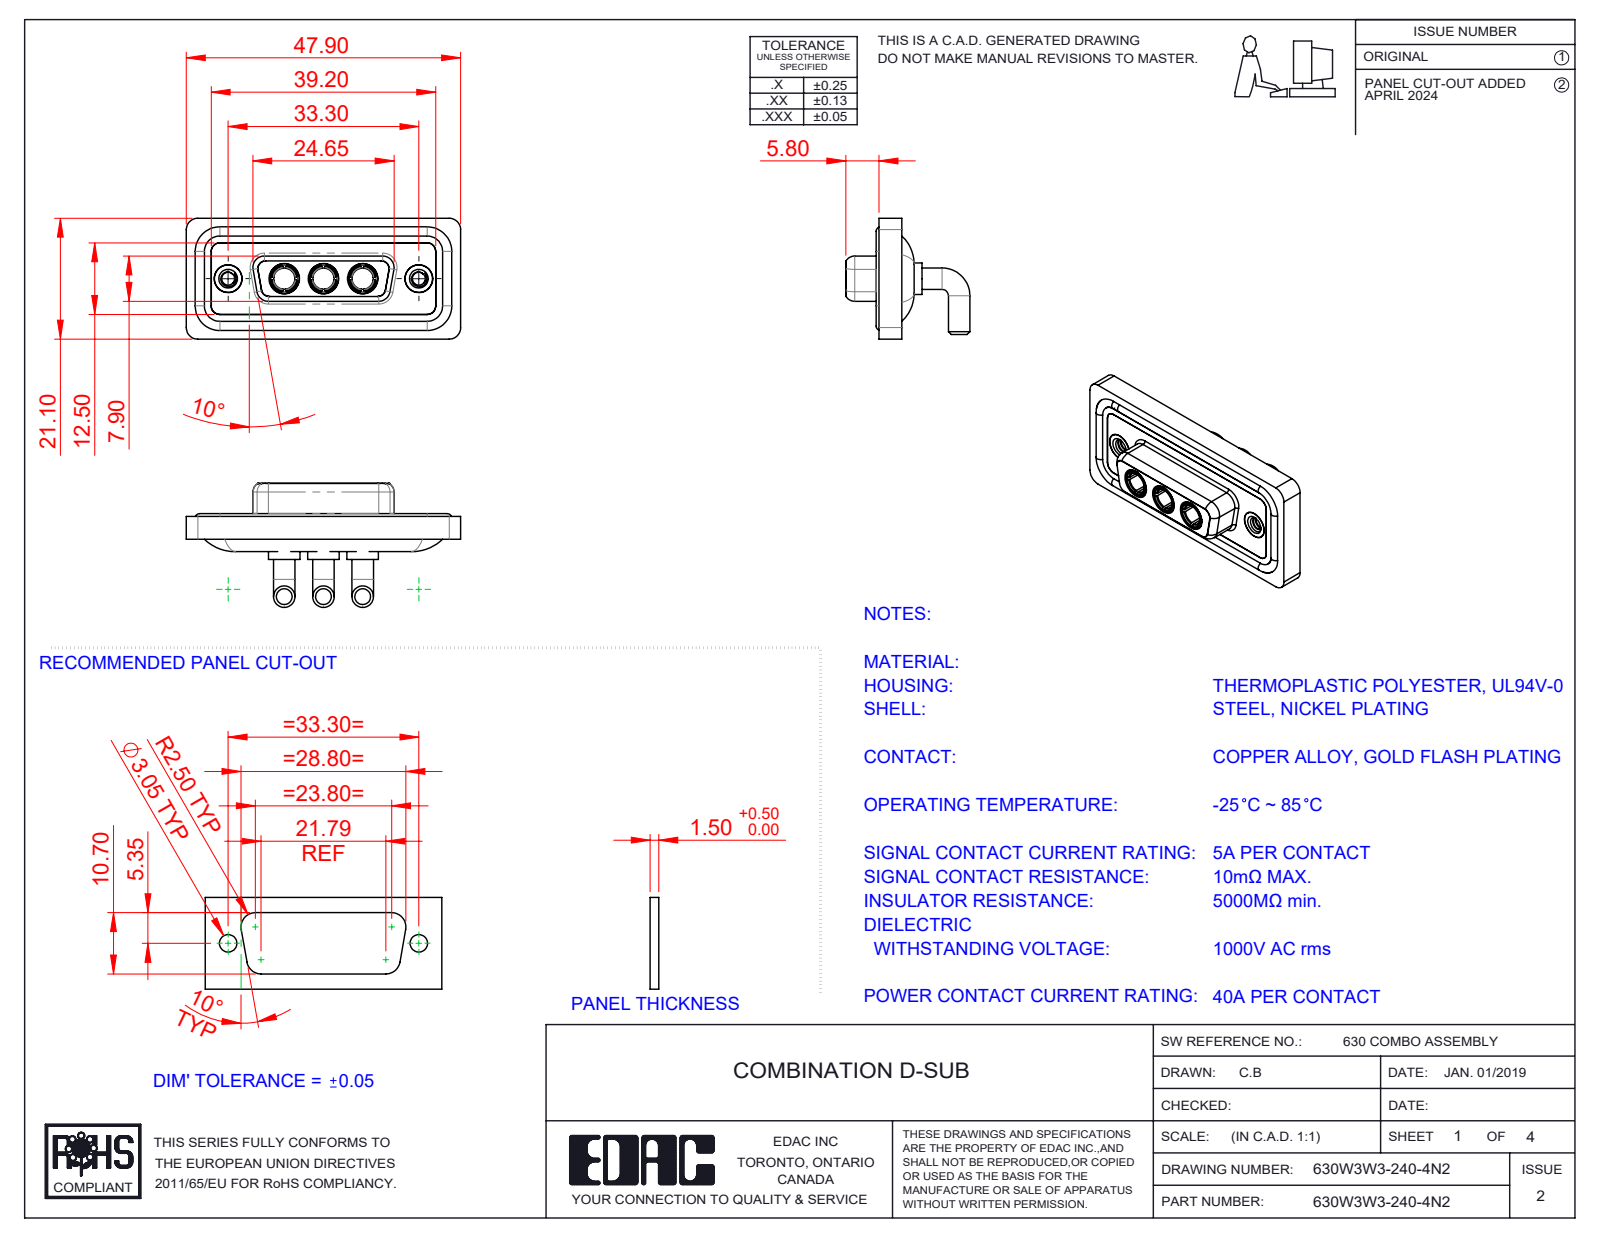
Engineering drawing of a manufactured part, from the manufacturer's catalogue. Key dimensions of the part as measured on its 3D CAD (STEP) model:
Part name (STEP PRODUCT): 630Combo Shell Rear_15 Contacts; 630Combo Waterproof Housing_15 Contacts; 630Combo Housing_3W3; Power Socket_40A RA (+3 more)
STEP written by: SolidWorks 2023 (CONFIG_CONTROL_DESIGN)
Units: millimetres
Bodies: 13 solids, 620 faces (192 planar, 263 cylindrical, 165 other)
Overall size (bounding box): 47.9 × 21.68 × 21.1
Volume: 6 398 mm³ · Surface area: 10 103 mm²
Round holes (diameter × count): ⌀4.85 ×5, ⌀3.7 ×3, ⌀5.3 ×3, ⌀2.26 ×2, ⌀4 ×2, ⌀4.05 ×2, ⌀5 ×2
Round bosses / shafts (diameter × count): ⌀3.75 ×6, ⌀1.6 ×4, ⌀5.5 ×3, ⌀5.2 ×3, ⌀4.96 ×3, ⌀4.75 ×3, ⌀4.95 ×2, ⌀4.8 ×2
Partial cylindrical surfaces — rounded edges, fillets, slot ends (radius × count): R2 ×20, R1.5 ×18, R1.35 ×12, R1.6 ×8, R0.25 ×4, R0.5 ×4, R0.6 ×4, R0.65 ×4
Main face-to-face distances: 0.4, 1.8, 1.1, 1.6, 2.9, 2.5, 3.1, 3.7, 4.1, 1.5
Hole centre spacings: 6.85, 9.8, 16.65, 23.5, 13.7, 33.3
